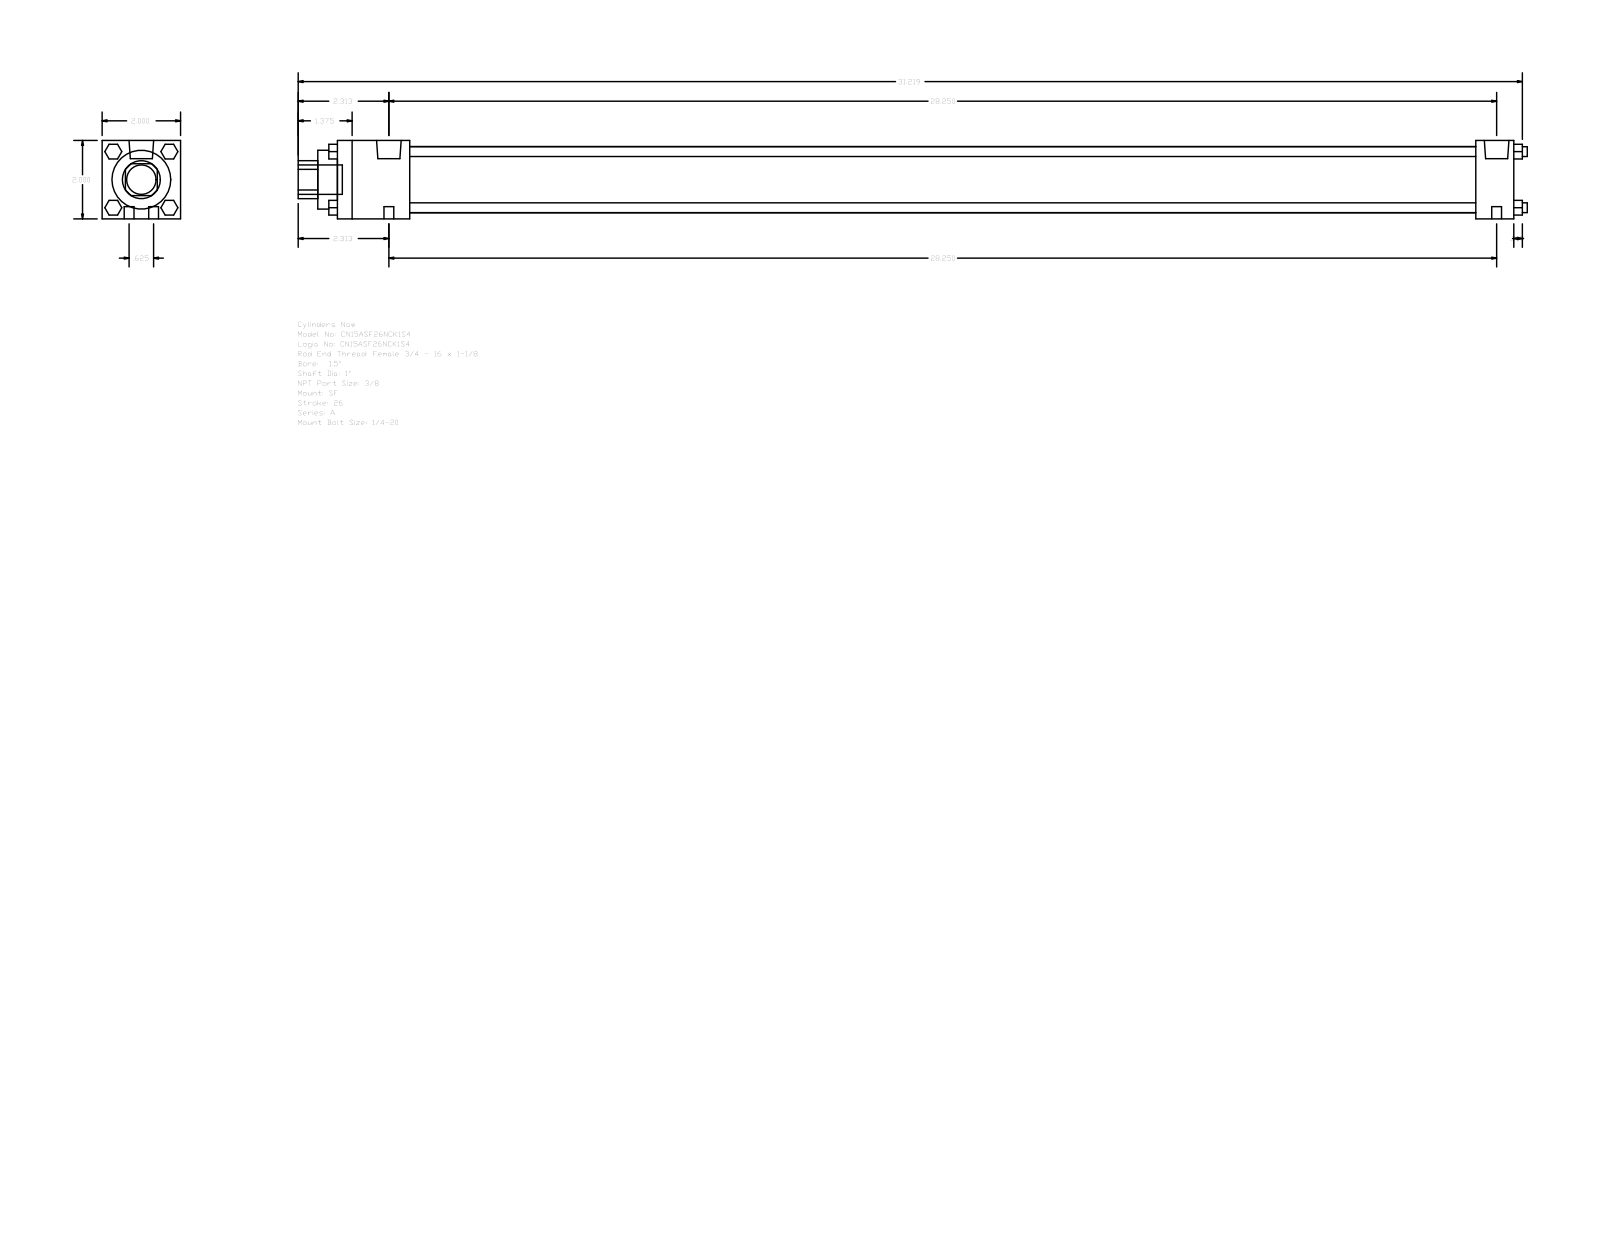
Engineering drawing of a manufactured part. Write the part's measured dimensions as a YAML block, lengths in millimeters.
part_name: "A_SF__0150_1"
step_written_by: "GSSL Pune (CONFIG_CONTROL_DESIGN)"
units: millimeters
bodies: {solids: 0, faces: 124, planar: 94, cylindrical: 30, other: 0}
overall_size: [796.13, 50.8, 50.8]
round_holes:
  - {diameter: 25.4, count: 1}
  - {diameter: 38.1, count: 1}
  - {diameter: 42.93, count: 1}
round_bosses_or_shafts:
  - {diameter: 6.35, count: 8}
  - {diameter: 15.93, count: 2}
  - {diameter: 5.56, count: 2}
  - {diameter: 19.05, count: 1}
partial_cylinders:
  - {radius: 12.29, count: 1}
face_to_face_distances: [50.8, 762, 46.83, 737.39, 690.56, 715.17, 24.61, 12.7, 59.53, 750.09]
